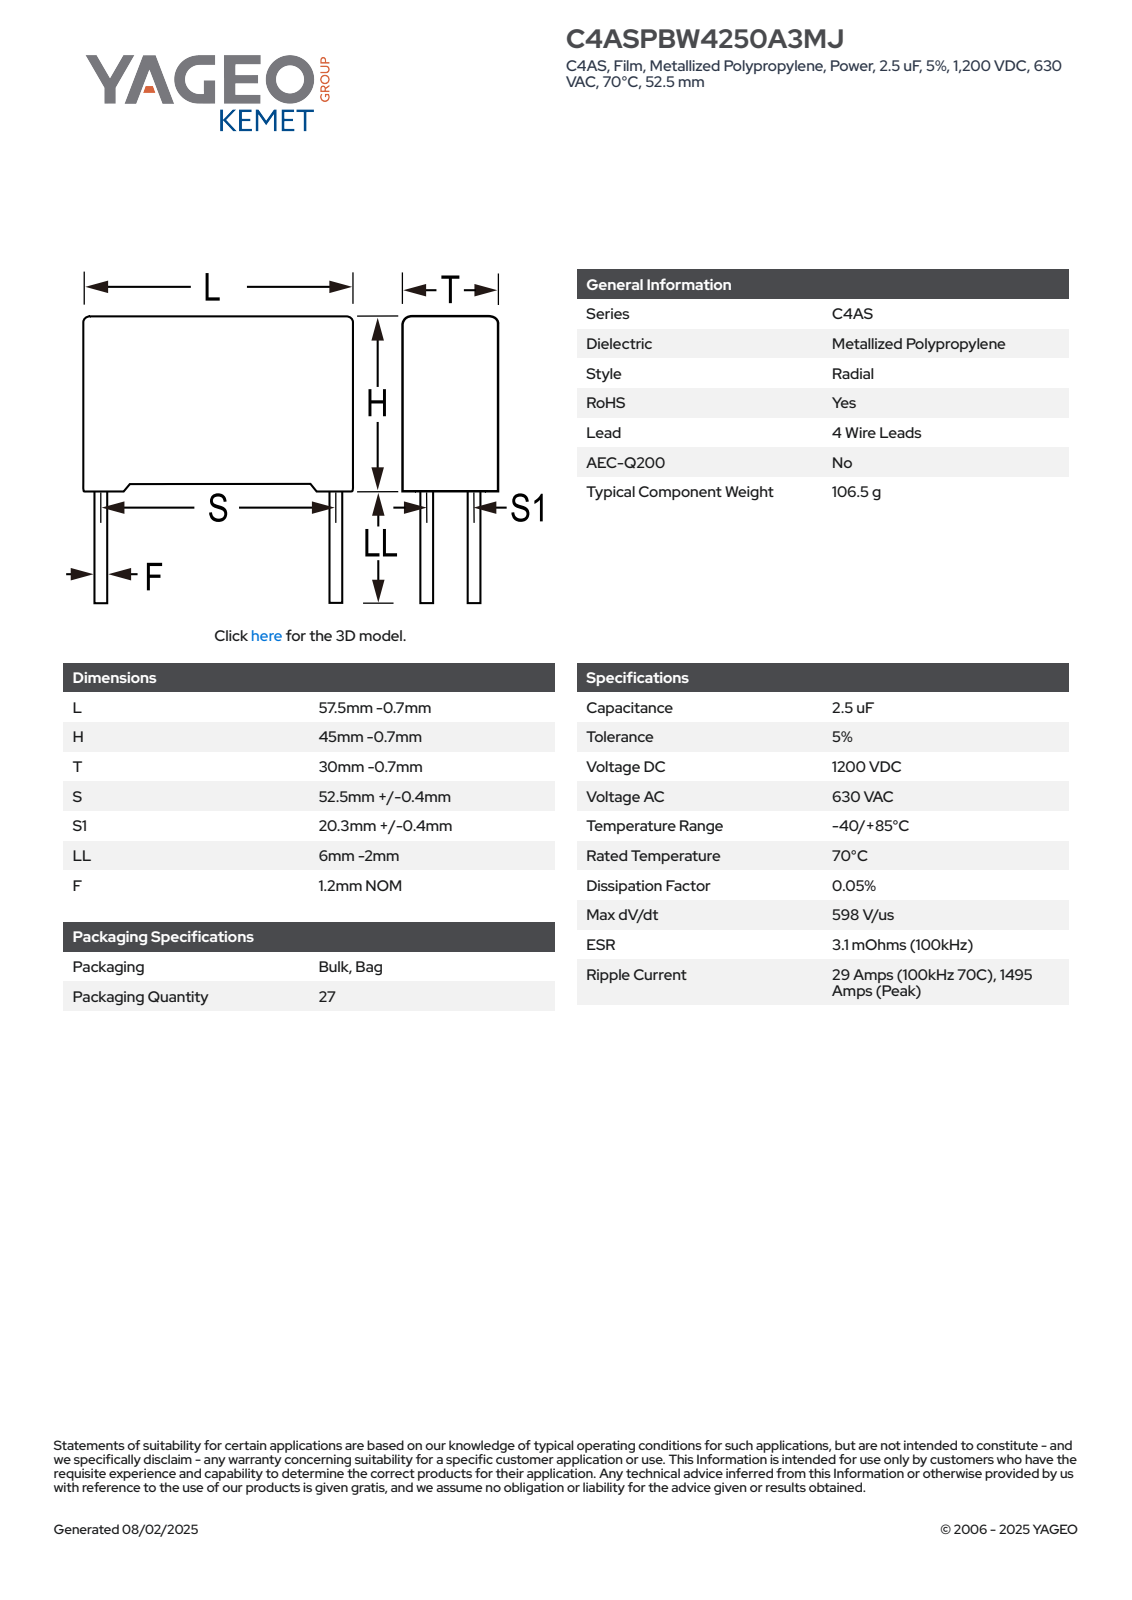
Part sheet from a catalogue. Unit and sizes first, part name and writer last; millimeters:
Units: millimetres
Overall size (bounding box): 56.8 × 48.3 × 29.3
Round bosses / shafts (diameter × count): ⌀1.2 ×4
Main face-to-face distances: 29.3, 43, 56.8, 1.3, 44.3, 1.8, 55, 53.2, 27.5, 25.7
Volume: 71 768 mm³ · Surface area: 11 222 mm²
Bodies: 4 solids, 91 faces (83 planar, 8 cylindrical, 0 other)
Part name (STEP PRODUCT): CFP_RB4_57.5X45X30_L56.8H44.3T29.3S52.5S120.3LL4F1.2
STEP written by: SolidWorks 2014 (AUTOMOTIVE_DESIGN)
